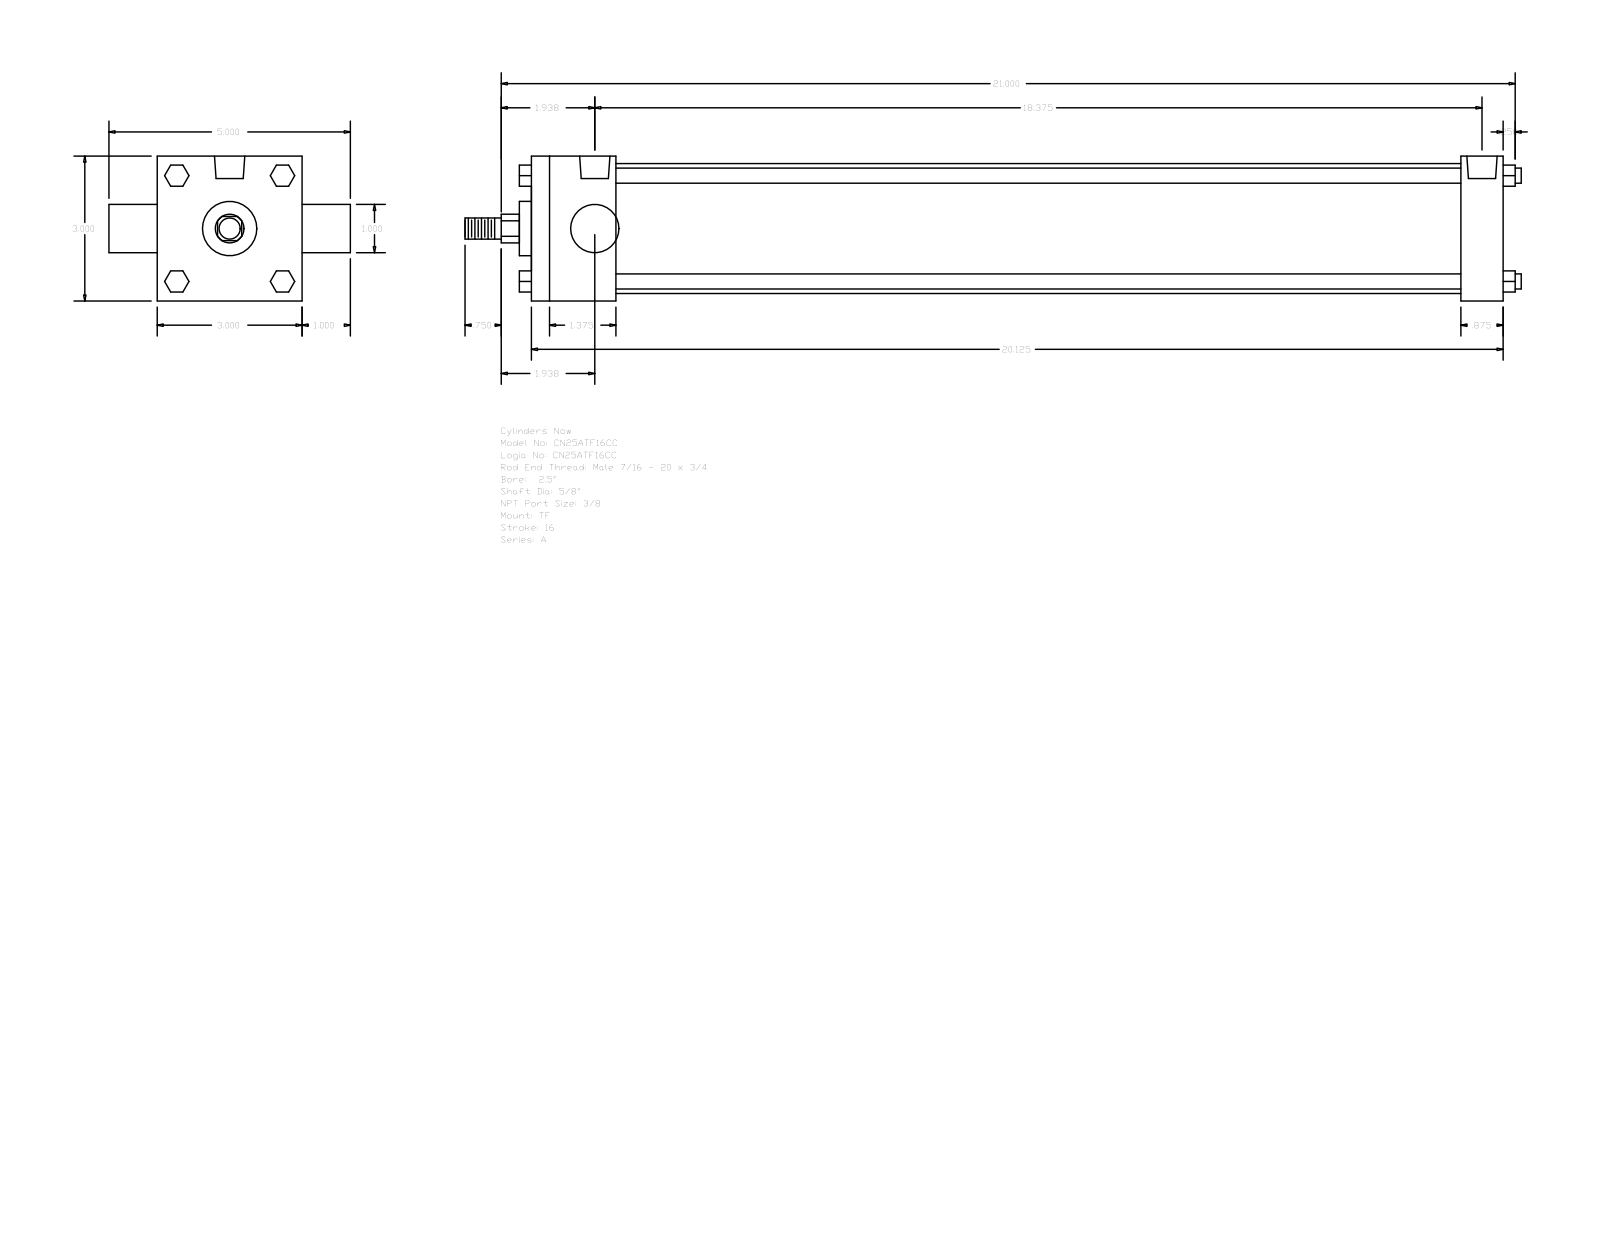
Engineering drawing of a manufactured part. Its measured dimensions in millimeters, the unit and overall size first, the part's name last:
Units: millimetres
Overall size (bounding box): 555.62 × 127 × 76.2
Round holes (diameter × count): ⌀5.56 ×3, ⌀15.93 ×2
Round bosses / shafts (diameter × count): ⌀7.94 ×4, ⌀68.33 ×1, ⌀28.57 ×1, ⌀25.4 ×1, ⌀15.88 ×1, ⌀11.11 ×1
Partial cylindrical surfaces — rounded edges, fillets, slot ends (radius × count): R7.54 ×1
Main face-to-face distances: 76.2, 511.17, 44.45, 488.94, 444.49, 466.72, 22.23, 25.4, 101.6, 6.35
Hole centre spacings: 2.38, 469.11, 466.73, 471.49
Bodies: 0 solids, 120 faces (92 planar, 28 cylindrical, 0 other)
Part name (STEP PRODUCT): A_TF__0250_0.625
STEP written by: GSSL Pune (CONFIG_CONTROL_DESIGN)
